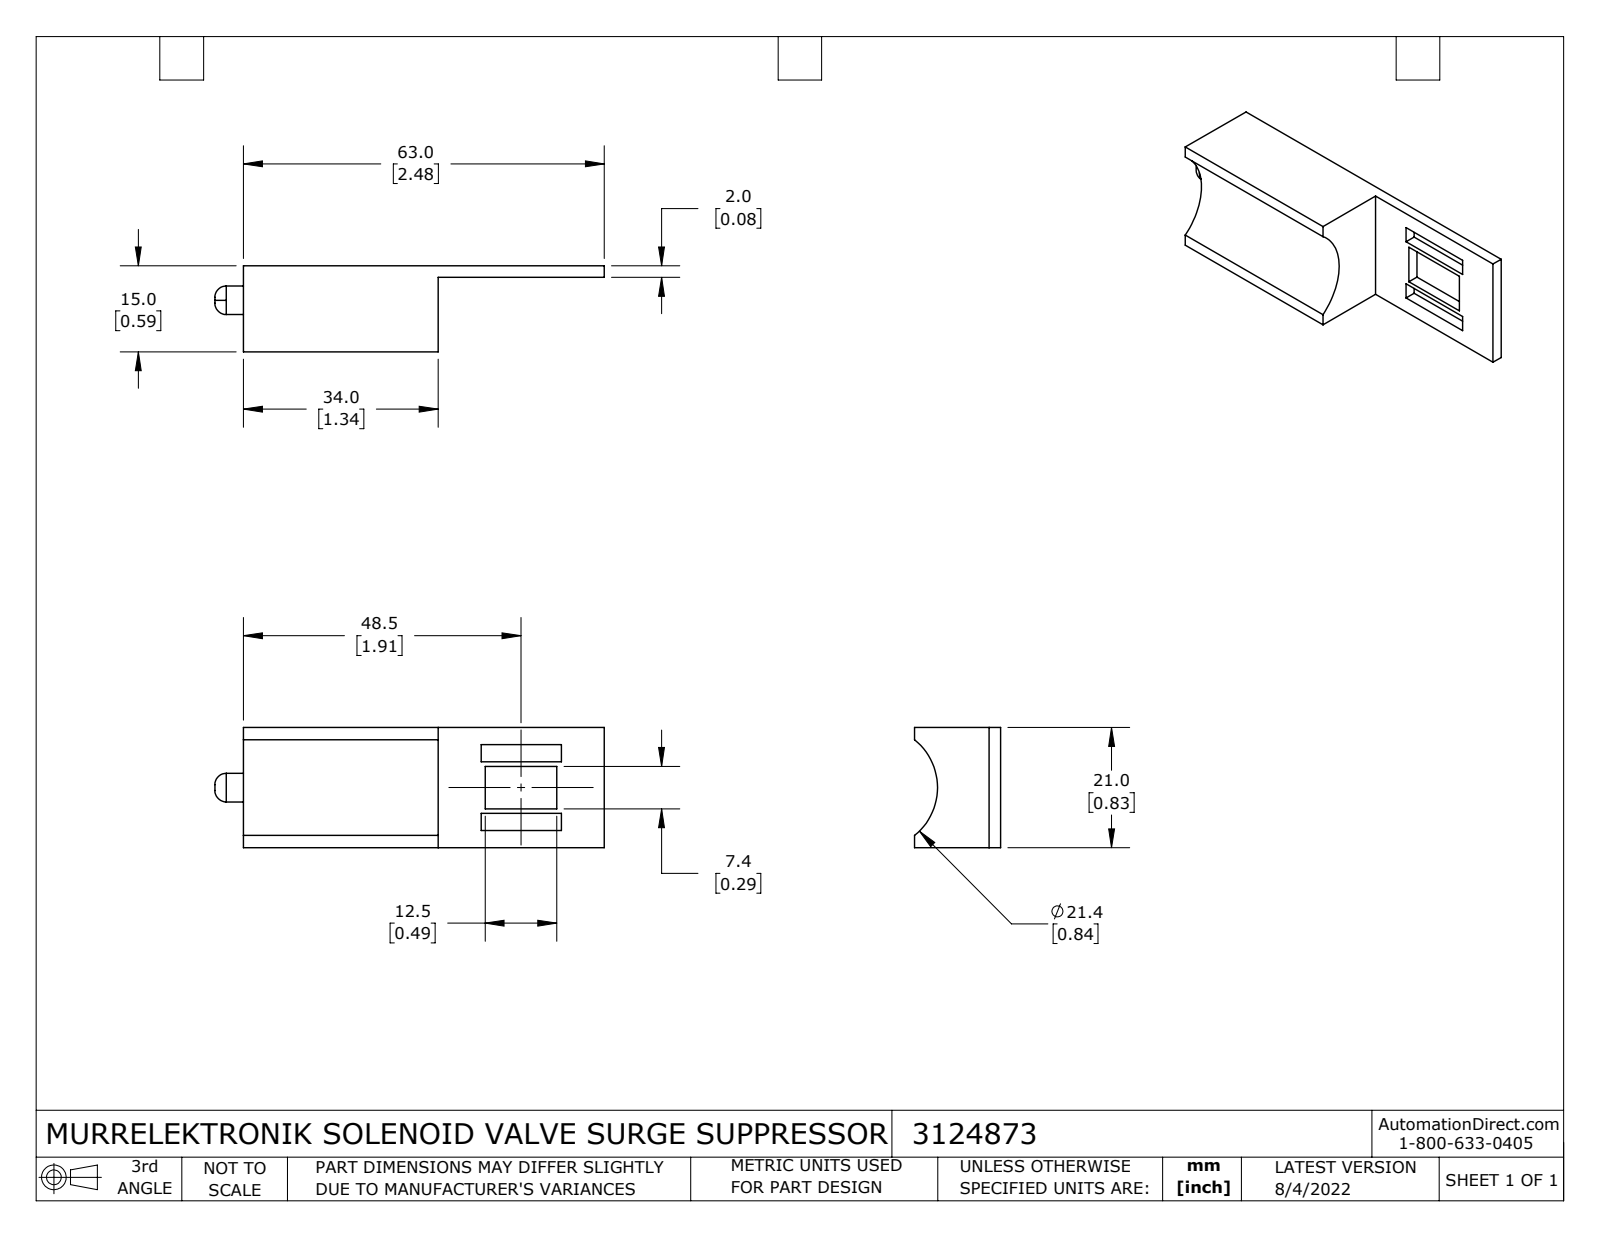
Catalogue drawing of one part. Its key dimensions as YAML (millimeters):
part_name: "3124873"
step_written_by: "SolidWorks 2021 (CONFIG_CONTROL_DESIGN)"
units: millimeters
bodies: {solids: 1, faces: 27, planar: 22, cylindrical: 3, other: 2}
overall_size: [68, 21, 15]
volume: 10082
surface_area: 4328
round_bosses_or_shafts:
  - {diameter: 5, count: 1}
partial_cylinders:
  - {radius: 10.7, count: 1}
face_to_face_distances: [21, 2, 15, 34, 13, 3, 8.2, 0.8, 6, 18]
